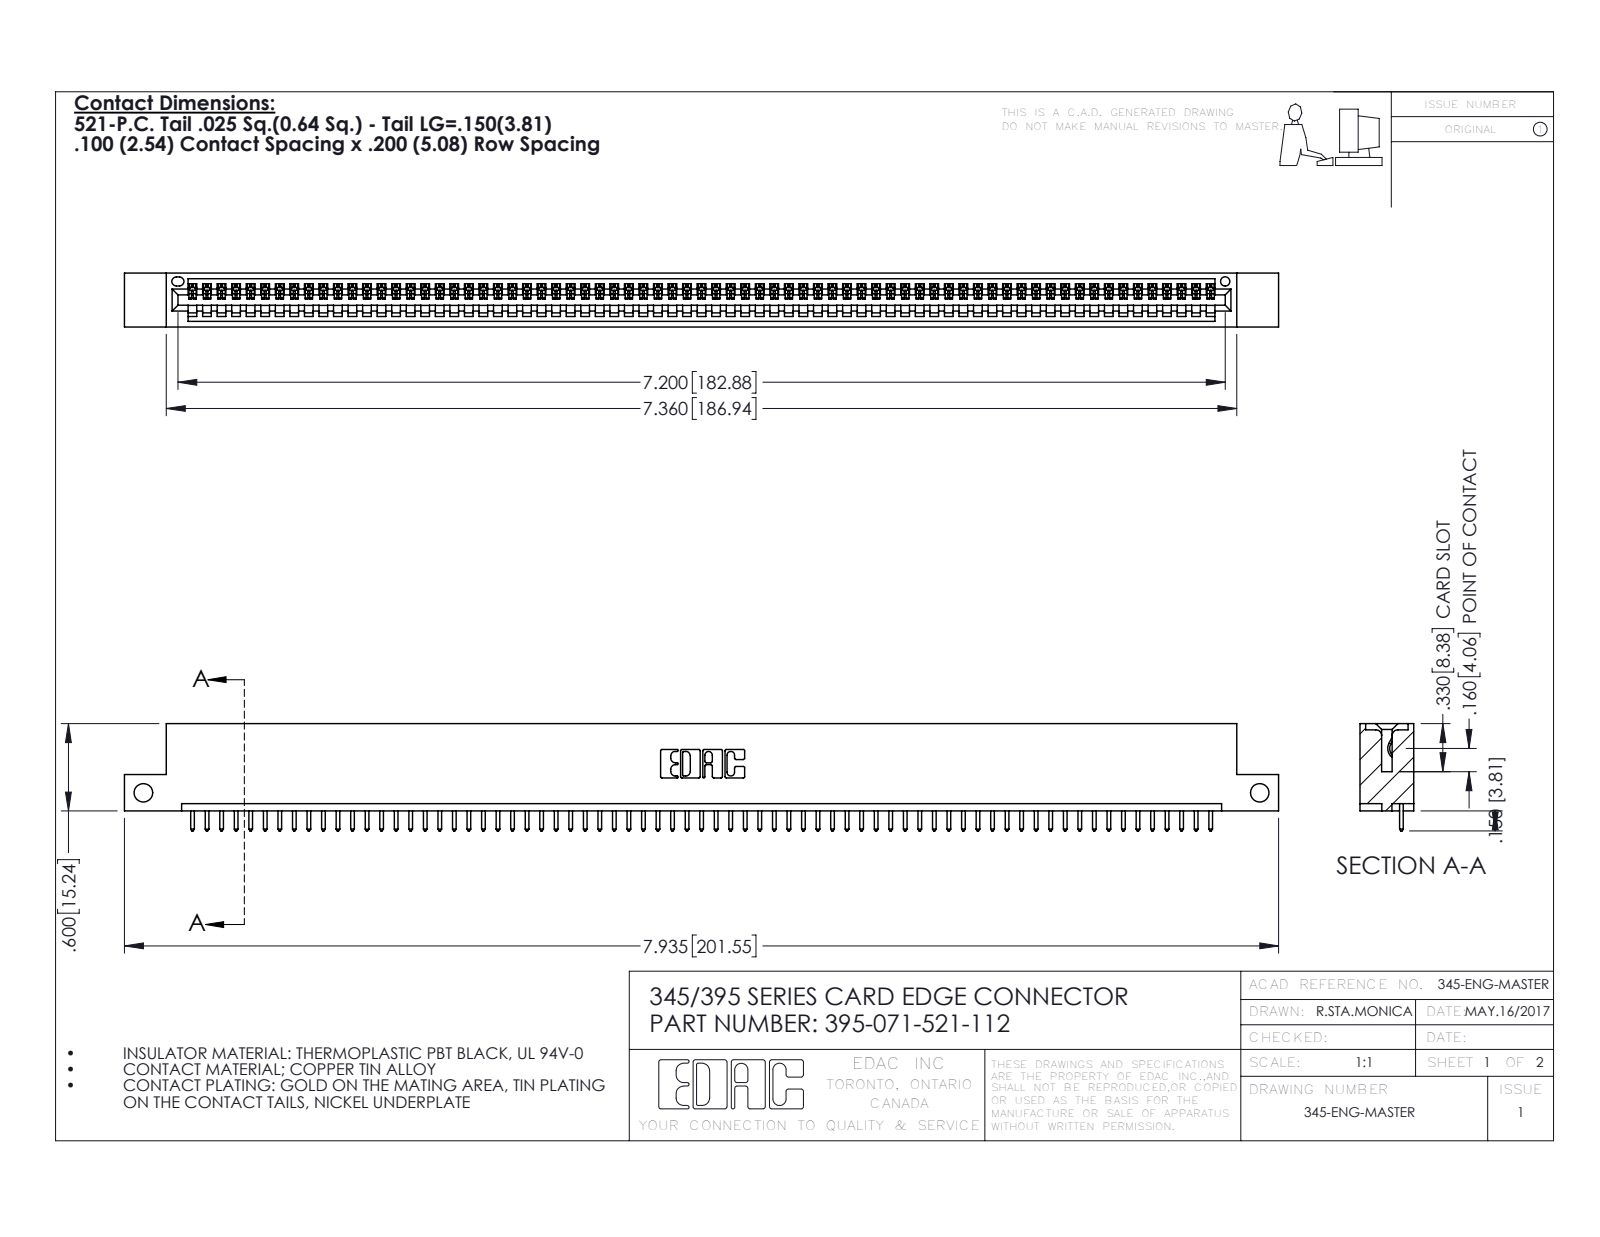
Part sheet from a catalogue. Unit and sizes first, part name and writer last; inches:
Units: inches
Overall size (bounding box): 7.935 × 0.737 × 0.37
Round holes (diameter × count): ⌀0.128 ×2, ⌀0.064 ×1
Partial cylindrical surfaces — rounded edges, fillets, slot ends (radius × count): R0.006 ×142, R0.01 ×142, R0.01 ×22, R0.007 ×6, R0.031 ×6, R0.026 ×3, R0.031 ×2, R0.04 ×2
Main face-to-face distances: 0.298, 0.072, 0.37, 0.2, 0.098, 0.272, 0.025, 0.225, 0.149, 0.072
Hole centre spacings: 7.675
Volume: 1.165 in³ · Surface area: 38.49 in²
Bodies: 72 solids, 4244 faces (2920 planar, 1324 cylindrical, 0 other)
Part name (STEP PRODUCT): 395-071-521-112; 345-292-001_345-293-121; 345 Part_Flush Mounting Lugs - Side Mount
STEP written by: SolidWorks 2016 (CONFIG_CONTROL_DESIGN)
